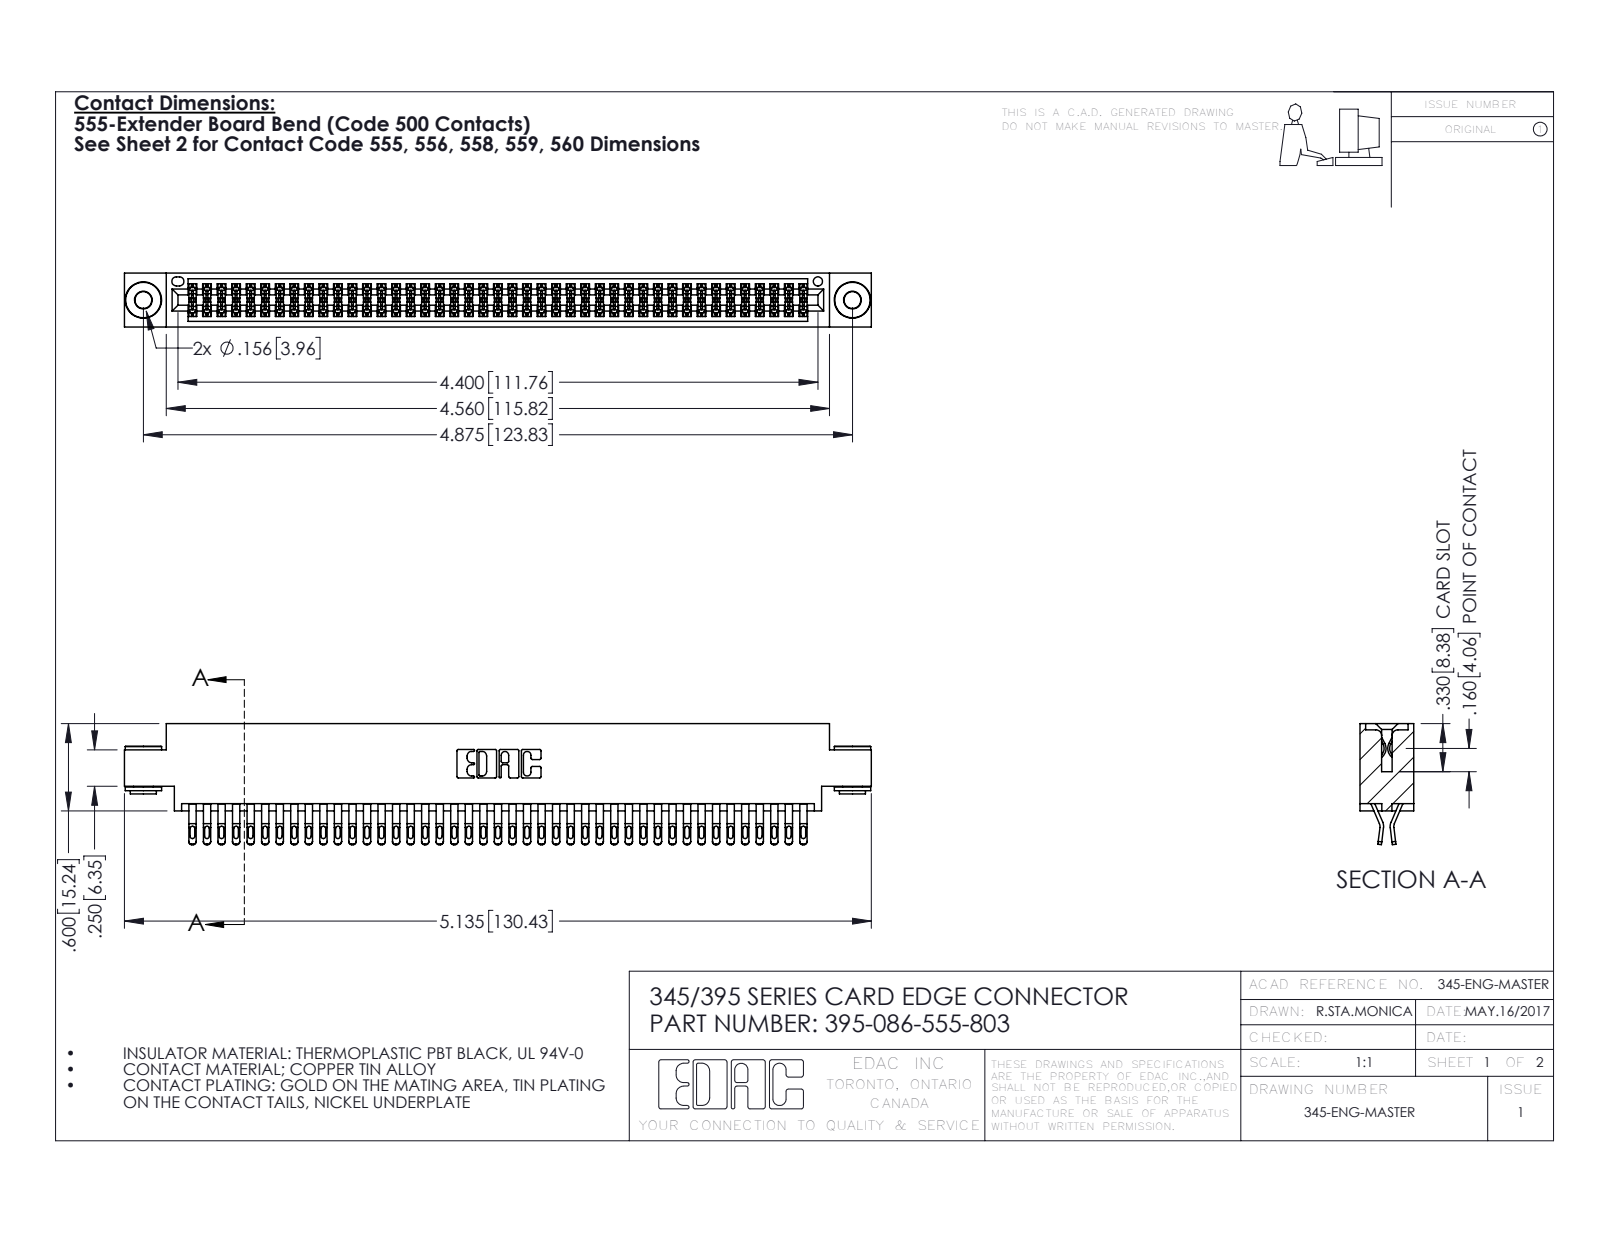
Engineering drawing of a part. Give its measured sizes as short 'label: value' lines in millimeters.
name: 395-086-555-803; 345 Part_0.170 Offset - 0.156 Dia-TH; 345-292-001_555 Tail; 345-250-002_345-250-002-102
written by: SolidWorks 2016 (CONFIG_CONTROL_DESIGN)
unit: mm
bodies: 89 solids, 4984 faces (2760 planar, 2216 cylindrical, 8 other)
size: 130.4 × 21.1 × 9.4
volume: 12 800 mm³; area: 20 210 mm²
holes: 2× ⌀2.9, 2× ⌀4, 1× ⌀1.6
bosses: 2× ⌀6.4, 2× ⌀4.6, 2× ⌀3.5
rounds: 215× R0.4, 172× R0.5, 129× R0.2, 22× R0.3, 6× R0.2, 6× R0.8, 3× R0.7, 2× R0.3
face distances: 1.8, 7.6, 9.4, 0.6, 5.1, 2.5, 6.9, 5.7, 4.4, 3.8
hole spacings: 6.9, 117.8, 123.8
